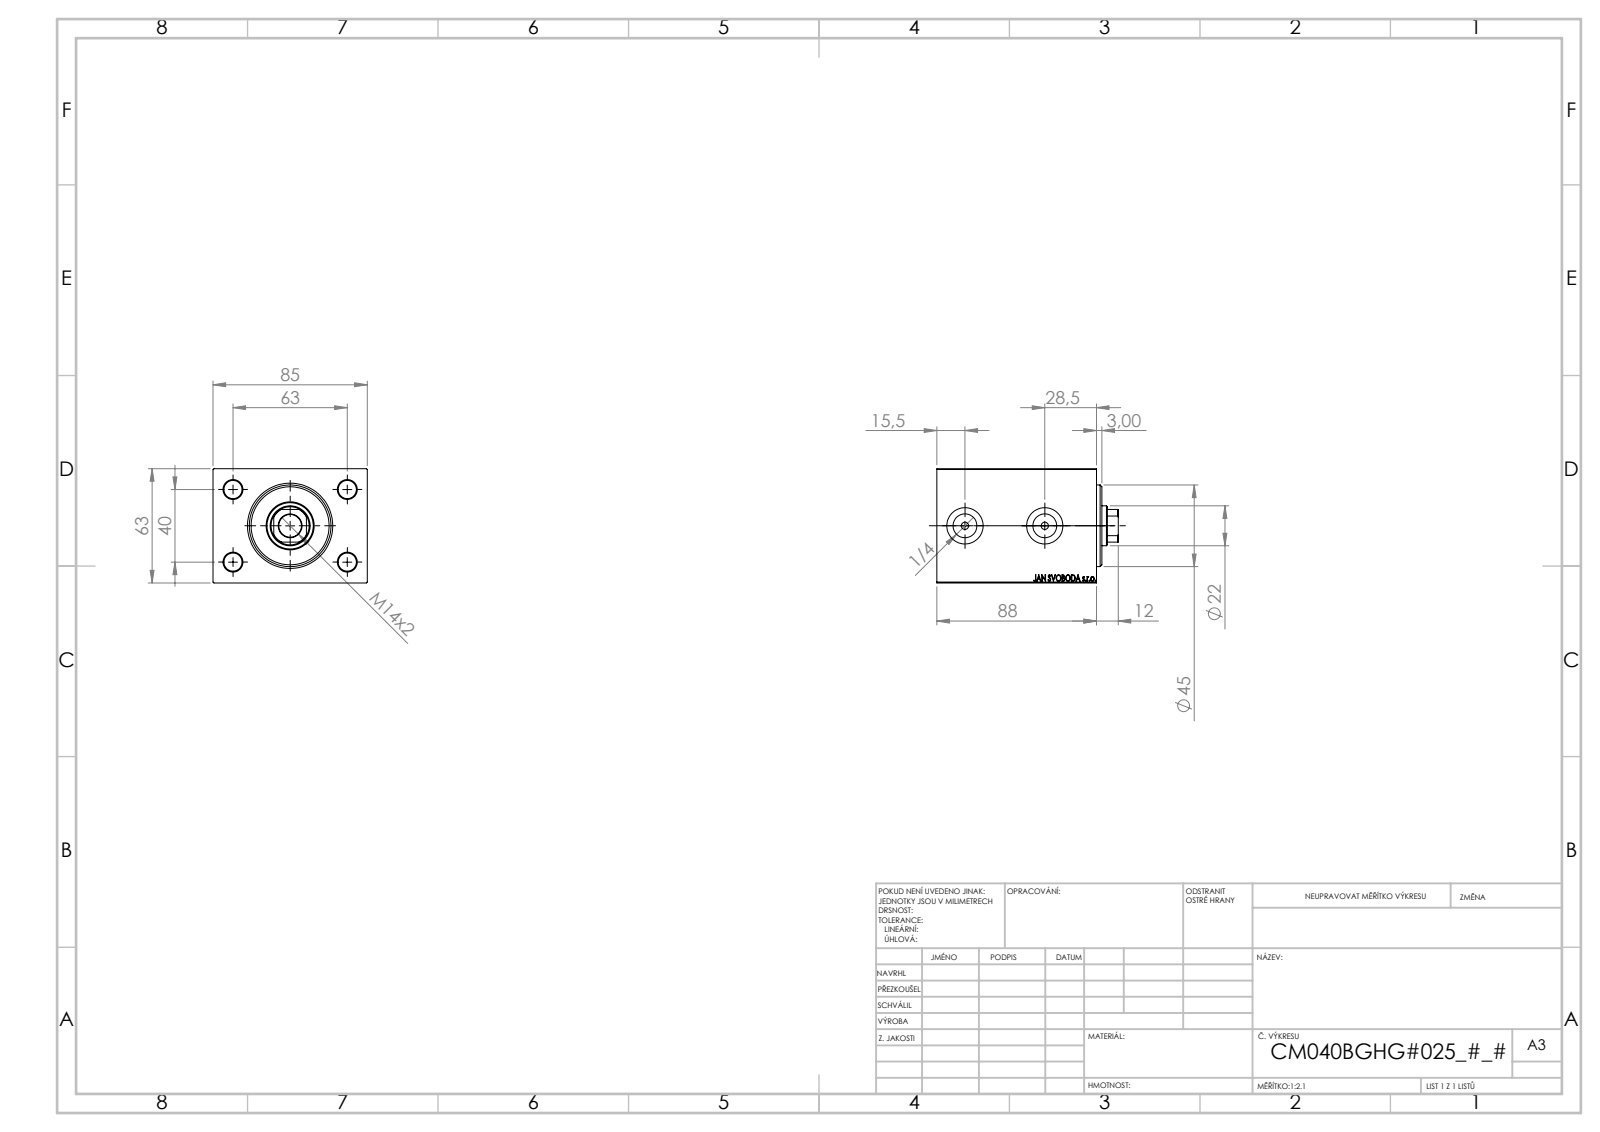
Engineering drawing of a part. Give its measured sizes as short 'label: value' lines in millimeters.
name: V450CM_B_Body; V450CM_VC_B; V450CM_B_VCP
written by: SolidWorks 2019 (CONFIG_CONTROL_DESIGN)
unit: mm
bodies: 3 solids, 881 faces (401 planar, 54 cylindrical, 426 other)
size: 100 × 85 × 63
volume: 437 100 mm³; area: 72 168 mm²
holes: 4× ⌀10, 2× ⌀4, 2× ⌀13.16, 2× ⌀20, 1× ⌀12.5, 1× ⌀22, 1× ⌀25.5, 1× ⌀26.5, 1× ⌀40, 1× ⌀42, 1× ⌀45
rounds: 1× R10.5
face distances: 63, 85, 88, 12, 76, 28.6, 47.4, 59.4, 3, 31.6
hole spacings: 37.31, 40, 63, 74.63, 44
